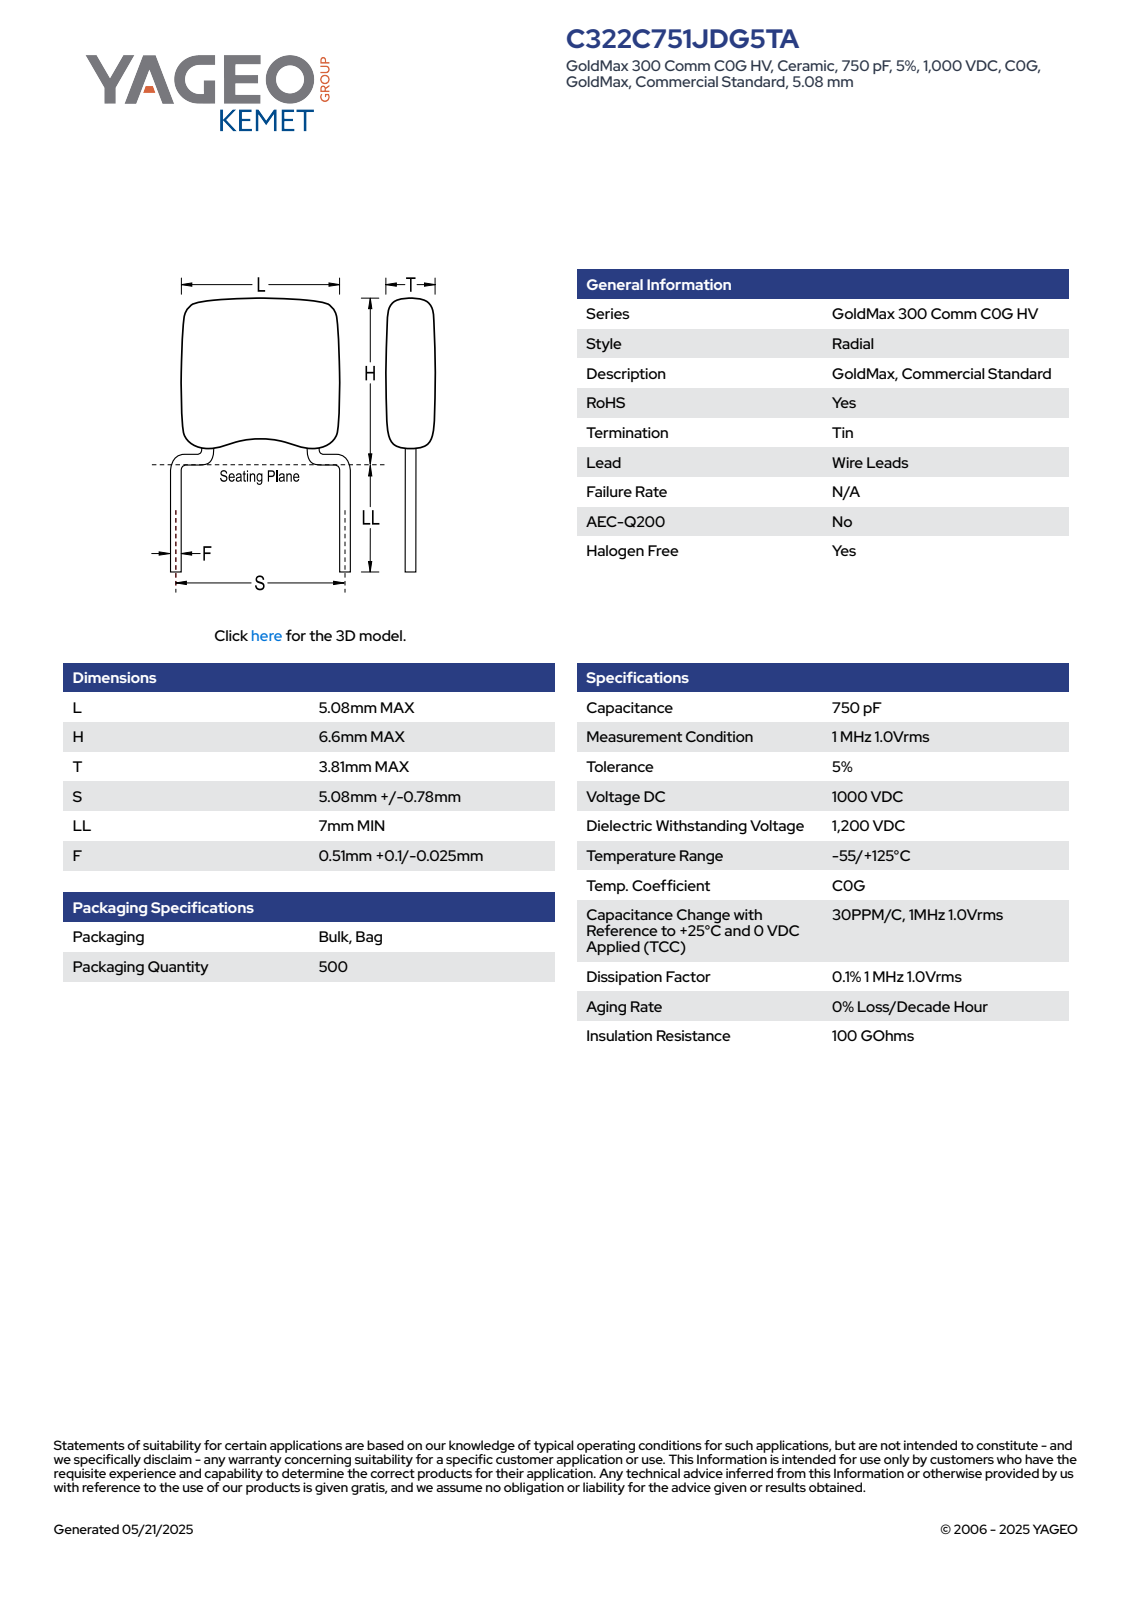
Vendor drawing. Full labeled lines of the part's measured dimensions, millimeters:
Part name (STEP PRODUCT): CCR_SB_5.08X6.6_L5.08H6.6T3.81S5.08LL7F0.51
STEP written by: SolidWorks 2014 (AUTOMOTIVE_DESIGN)
Units: millimetres
Bodies: 4 solids, 97 faces (65 planar, 14 cylindrical, 18 other)
Overall size (bounding box): 13.6 × 5.59 × 3.81
Volume: 88 mm³ · Surface area: 134 mm²
Round bosses / shafts (diameter × count): ⌀0.51 ×2
Partial cylindrical surfaces — rounded edges, fillets, slot ends (radius × count): R1 ×10
Main face-to-face distances: 3.81, 5.08, 4.81, 0.43, 2.64, 2.17, 2.21, 2.6, 0.39, 0.35
